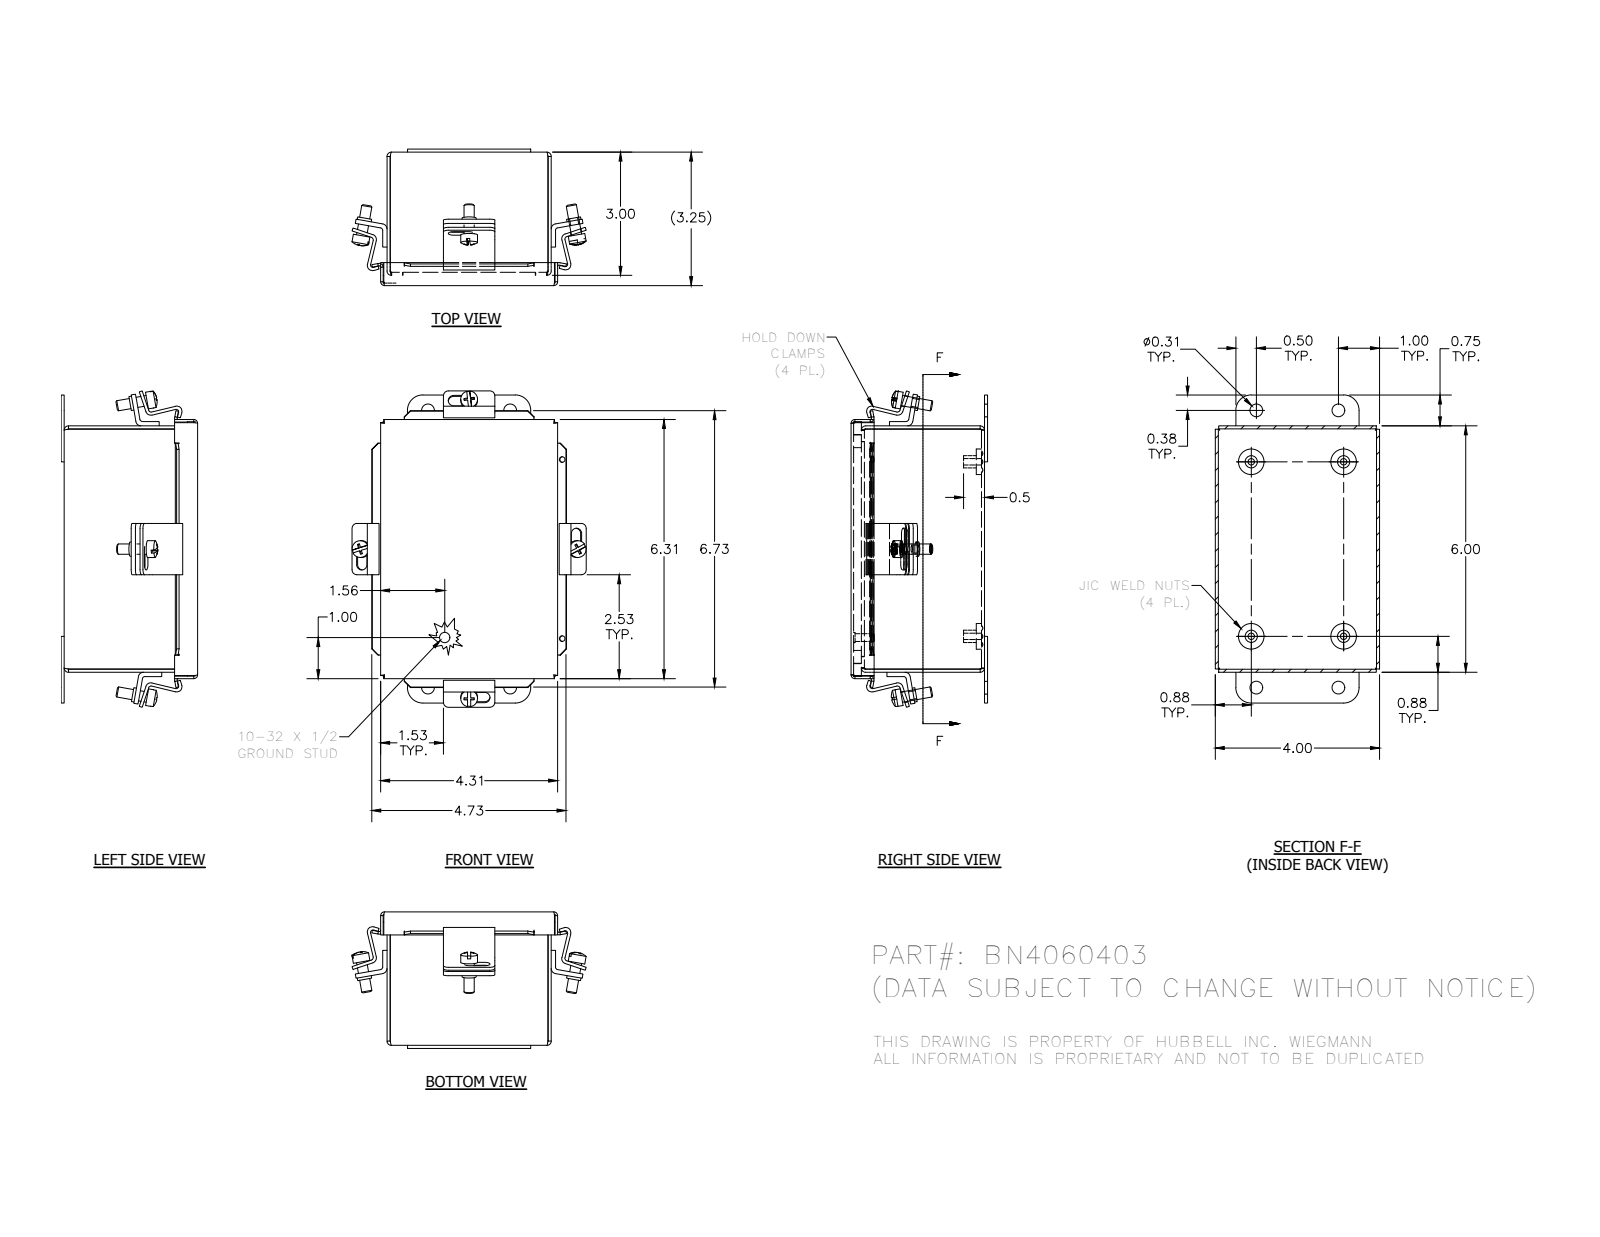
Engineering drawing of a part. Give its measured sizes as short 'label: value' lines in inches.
name: BN4060403BKP_1; BN40604LID_1; C2002_1; 3481_1 (+6 more)
written by: SolidWorks 2014 (AUTOMOTIVE_DESIGN)
unit: in
bodies: 23 solids, 537 faces (295 planar, 172 cylindrical, 70 other)
size: 7.704 × 5.705 × 3.324
volume: 13.25 in³; area: 346.6 in²
holes: 4× ⌀0.156, 4× ⌀0.196, 4× ⌀0.31, 2× ⌀0.136
bosses: 5× ⌀0.25, 4× ⌀0.625, 4× ⌀0.41, 4× ⌀0.344, 4× ⌀0.3, 1× ⌀0.19
rounds: 16× R0.031, 16× R0.125, 12× R0.063, 12× R0.126, 8× R0.093, 8× R0.105, 8× R0.133, 4× R0.375
face distances: 0.074, 0.062, 3.926, 3.187, 3.25, 3.113, 3.176, 5.926, 2.926, 4
hole spacings: 1.256, 5.502, 2, 2.25, 2.465, 2.466, 4.25, 4.809
